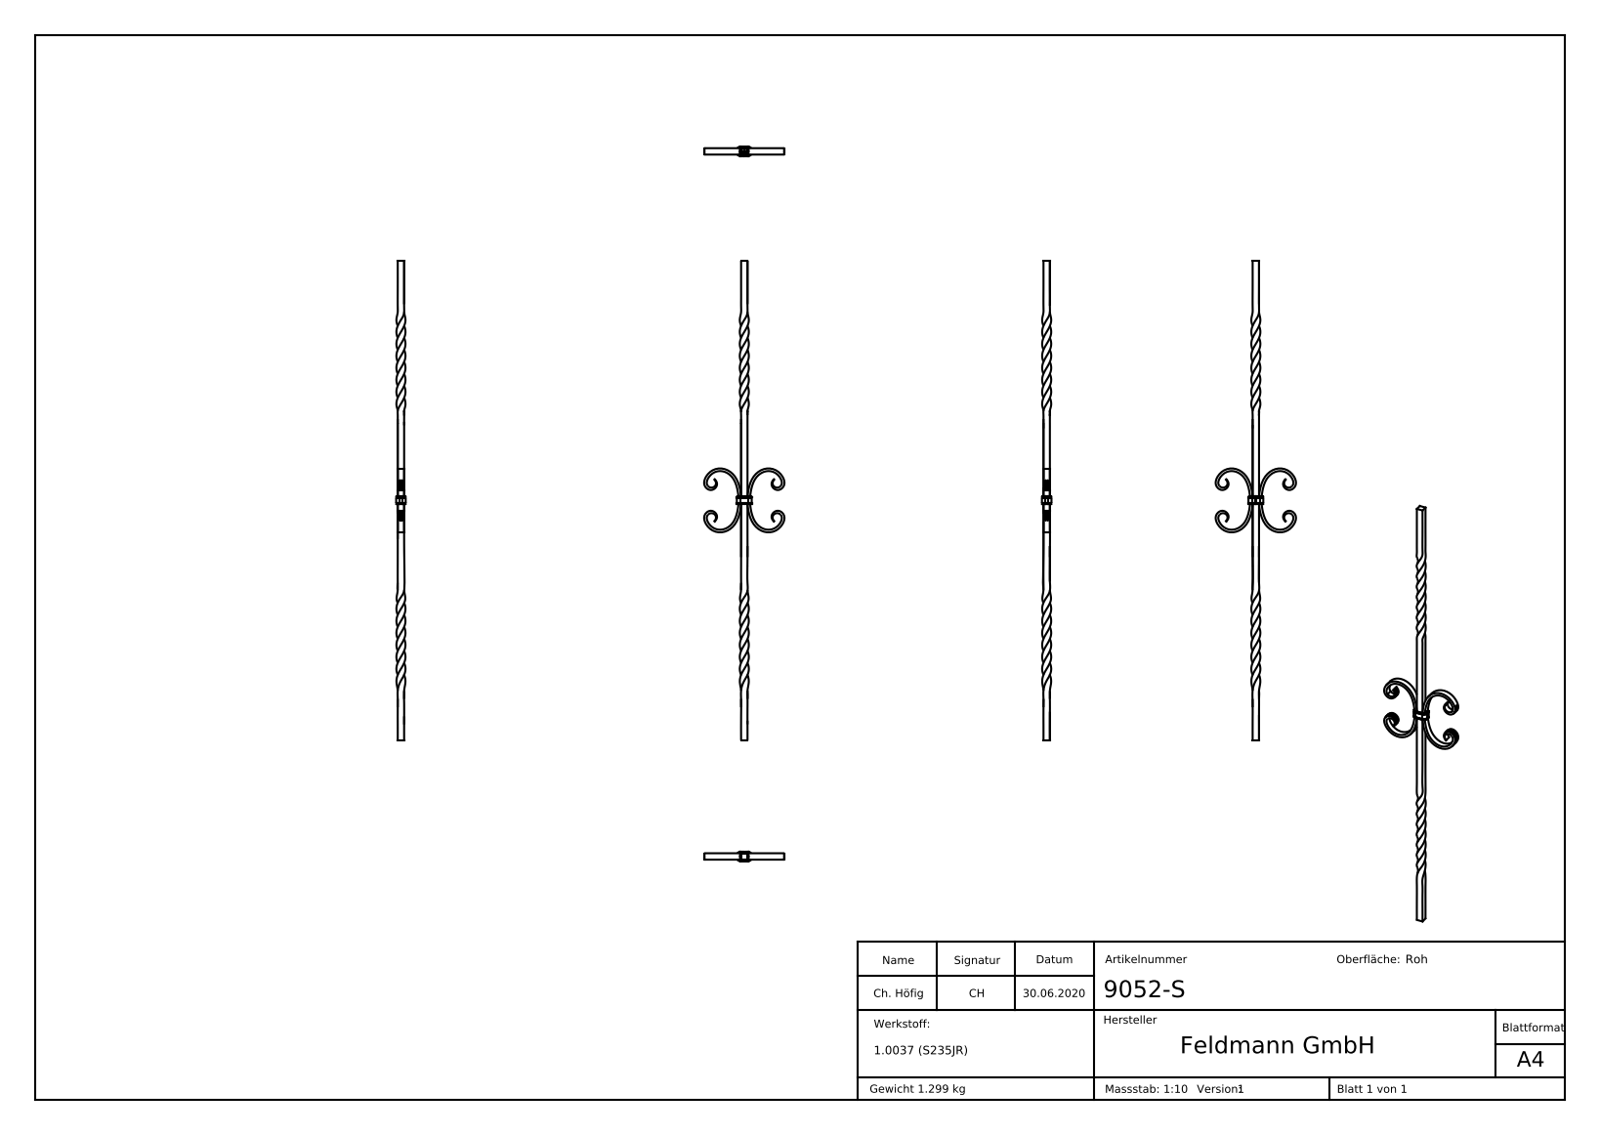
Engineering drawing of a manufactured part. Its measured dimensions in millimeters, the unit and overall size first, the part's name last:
Units: millimetres
Overall size (bounding box): 900 × 150.84 × 18.07
Partial cylindrical surfaces — rounded edges, fillets, slot ends (radius × count): R1 ×16, R0.25 ×8, R3.9 ×4, R4 ×4, R6.9 ×4, R25.25 ×4
Main face-to-face distances: 12, 12.07, 900, 443, 457, 2, 14, 3, 16.98, 4.98
Volume: 173 601 mm³ · Surface area: 67 836 mm²
Bodies: 4 solids, 382 faces (159 planar, 60 cylindrical, 163 other)
Part name (STEP PRODUCT): 9052-S Teil3; 9052-S; 9052-S Teil1; 9052-S Teil2
STEP written by: SolidWorks 2018 (CONFIG_CONTROL_DESIGN)
